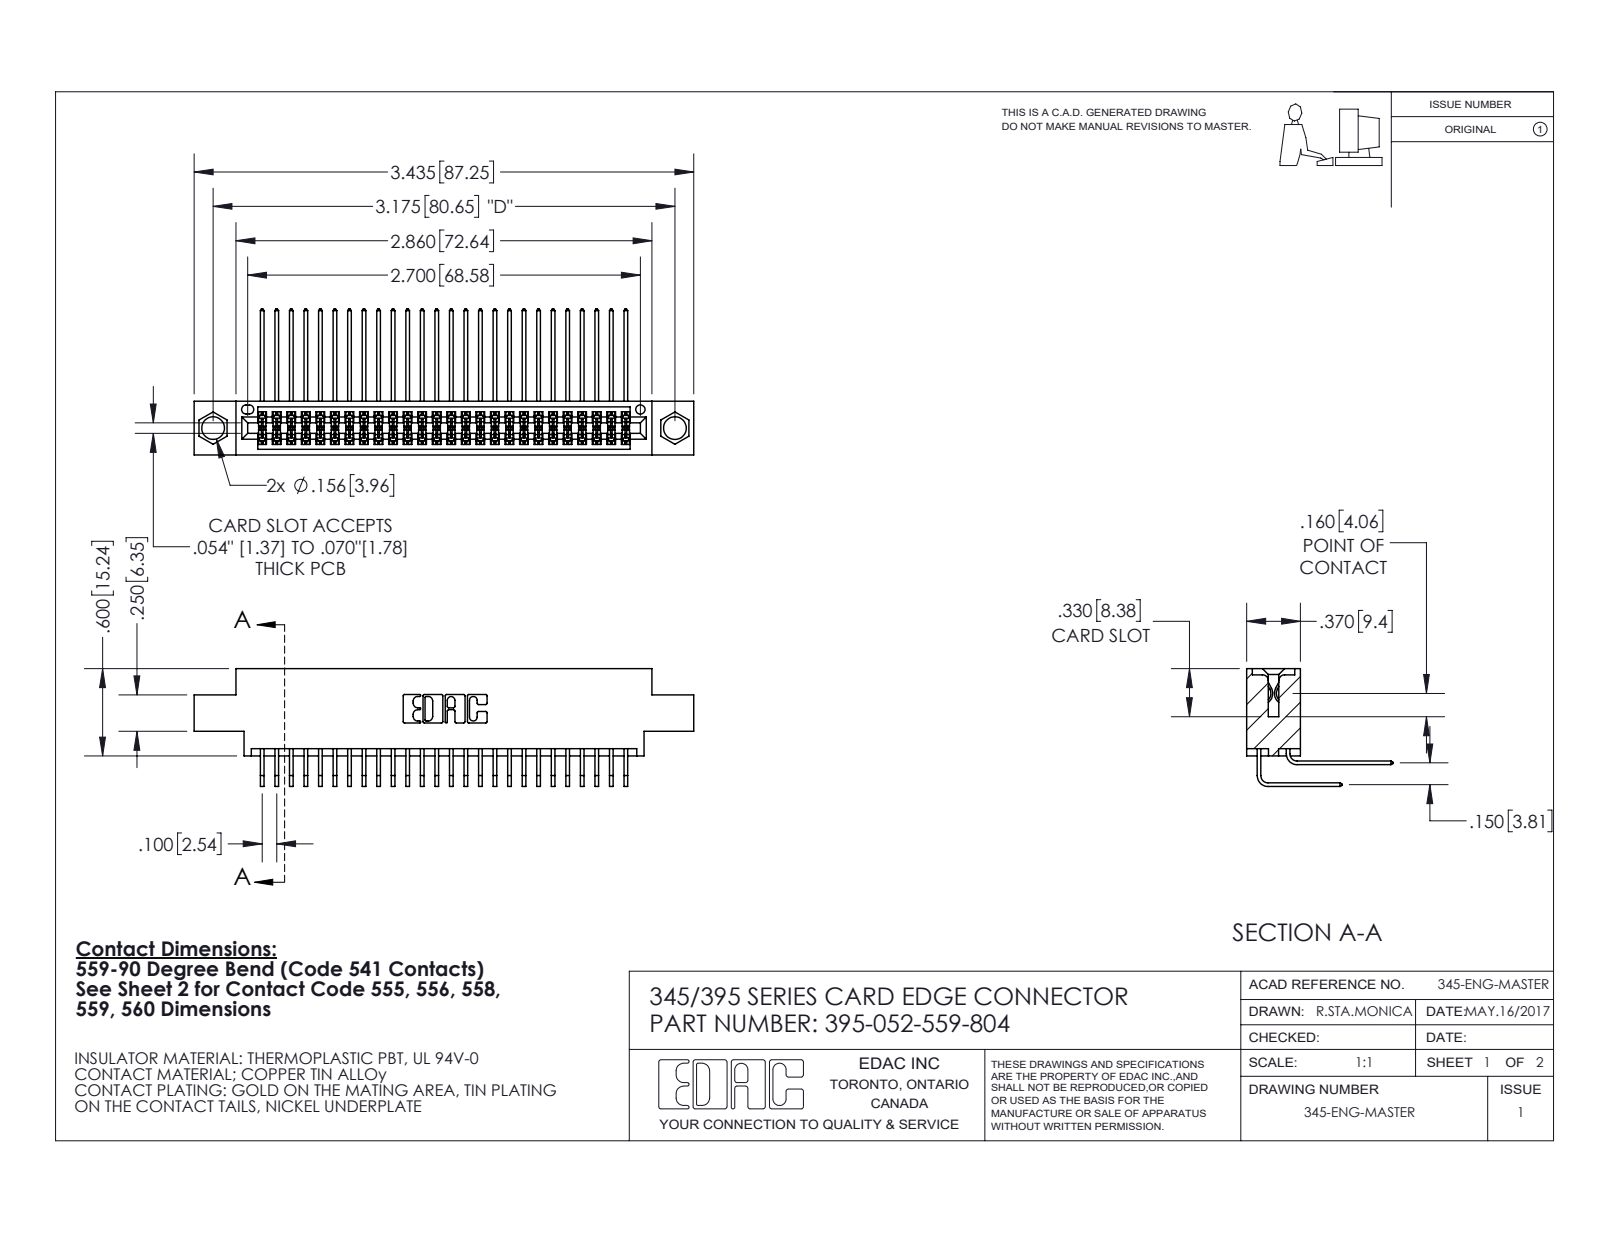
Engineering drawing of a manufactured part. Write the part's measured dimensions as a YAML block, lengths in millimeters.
part_name: "345-292-001_559 Tail - 2; 395-052-559-804; 345-292-001_558 559 Tail - 1; 345 Part_0.170 Offset - 0.156 Dia-TI"
step_written_by: "SolidWorks 2020 (CONFIG_CONTROL_DESIGN)"
units: millimeters
bodies: {solids: 53, faces: 2848, planar: 1918, cylindrical: 930, other: 0}
overall_size: [87.2, 25.5, 20.5]
volume: 8410
surface_area: 13520
round_holes:
  - {diameter: 4, count: 2}
  - {diameter: 1.6, count: 1}
partial_cylinders:
  - {radius: 0.2, count: 104}
  - {radius: 0.3, count: 22}
  - {radius: 0.2, count: 6}
  - {radius: 0.8, count: 6}
  - {radius: 0.7, count: 3}
  - {radius: 0.4, count: 2}
  - {radius: 0.5, count: 2}
  - {radius: 0.6, count: 2}
face_to_face_distances: [1.8, 7.6, 9.4, 5.1, 2.5, 6.9, 0.6, 3.8, 5.7, 4.4]
hole_center_spacings: [6.9, 74.7, 80.6]
